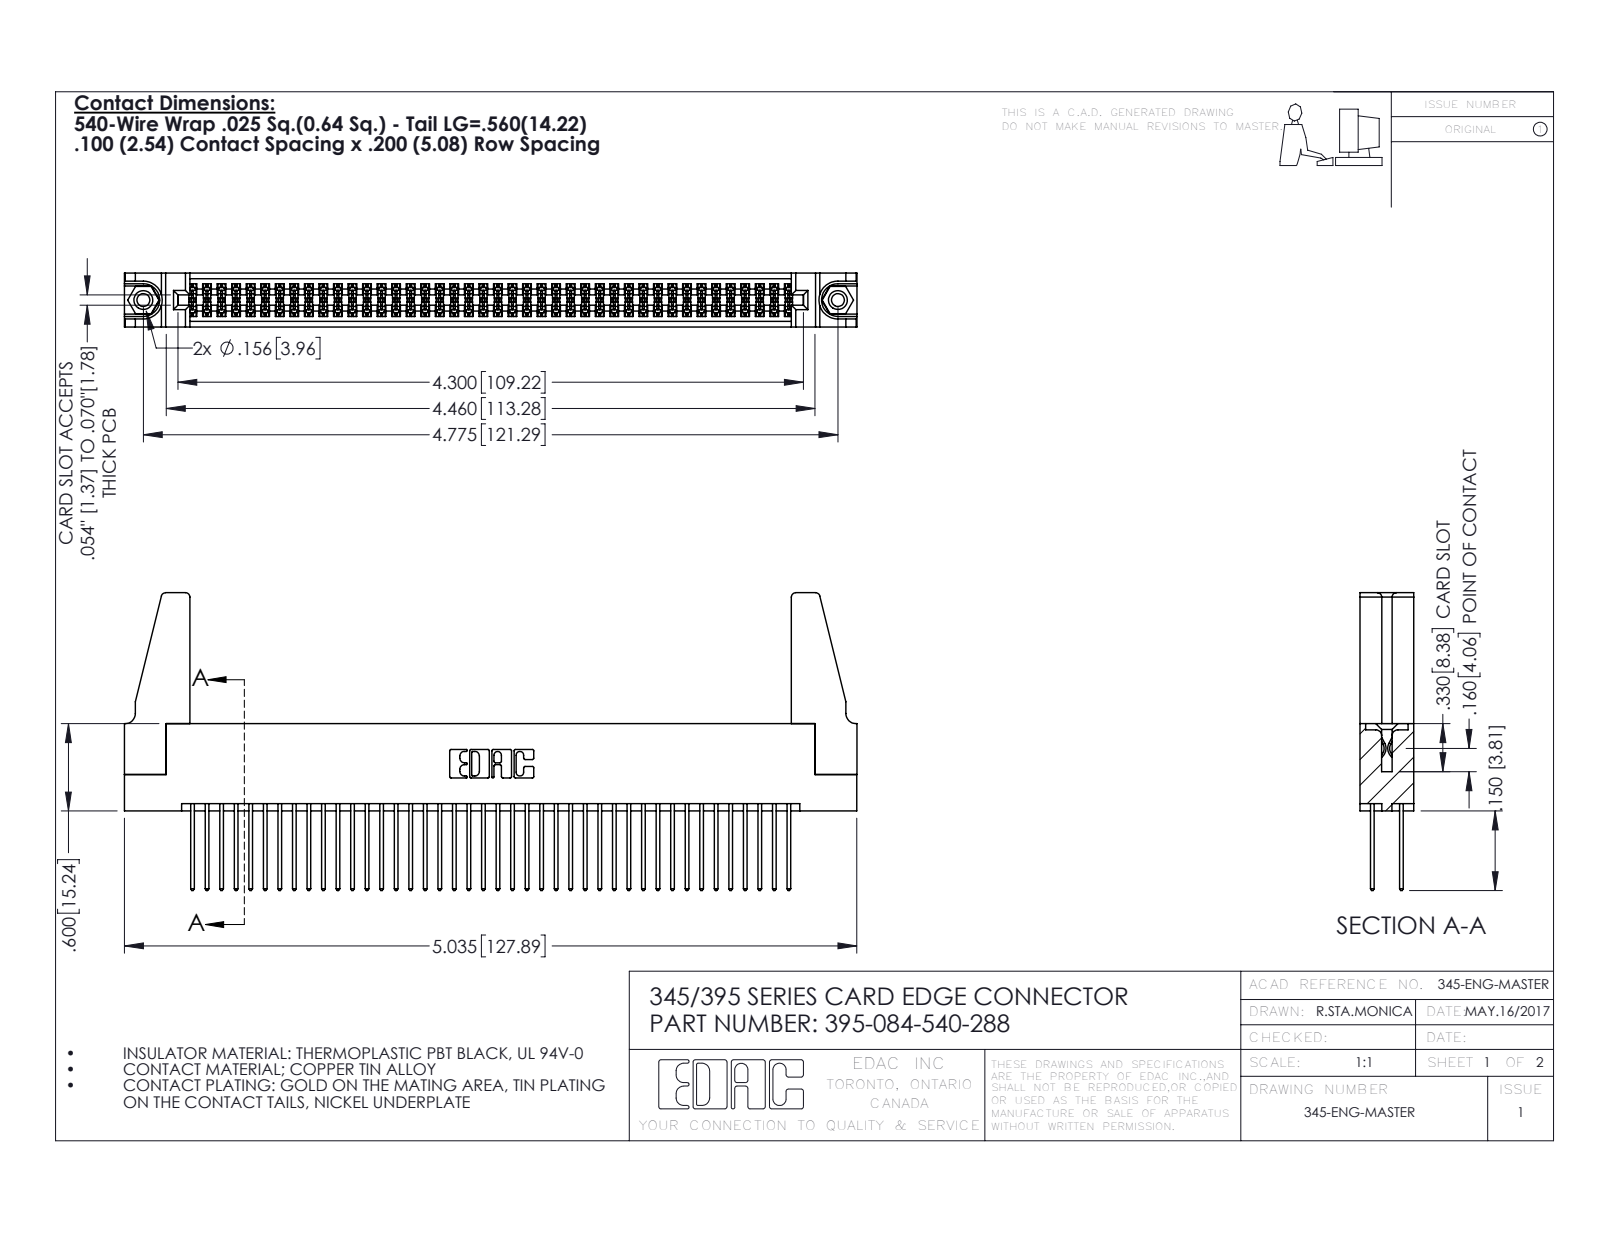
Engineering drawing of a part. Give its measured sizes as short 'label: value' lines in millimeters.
name: 345 Part_Flush Mounting Lugs - 0.156 Dia-TH; 345-220-078_345-220-088; 345-250-001_345-250-001-102; 345-292-001_345-293-140 (+1 more)
written by: SolidWorks 2016 (CONFIG_CONTROL_DESIGN)
unit: mm
bodies: 89 solids, 4450 faces (2924 planar, 1510 cylindrical, 16 other)
size: 127.9 × 52 × 9.4
volume: 16 000 mm³; area: 23 440 mm²
holes: 2× ⌀2.3, 2× ⌀3.2, 2× ⌀4, 1× ⌀1.6
bosses: 2× ⌀3.9
rounds: 126× R0.2, 84× R0.3, 22× R0.3, 8× R0.8, 6× R0.2, 6× R0.8, 3× R0.7, 2× R0.4
face distances: 1.8, 7.6, 5.1, 2.5, 6.9, 0.6, 9.4, 5.7, 4.4, 3.8
hole spacings: 6.9, 115.3, 121.3
